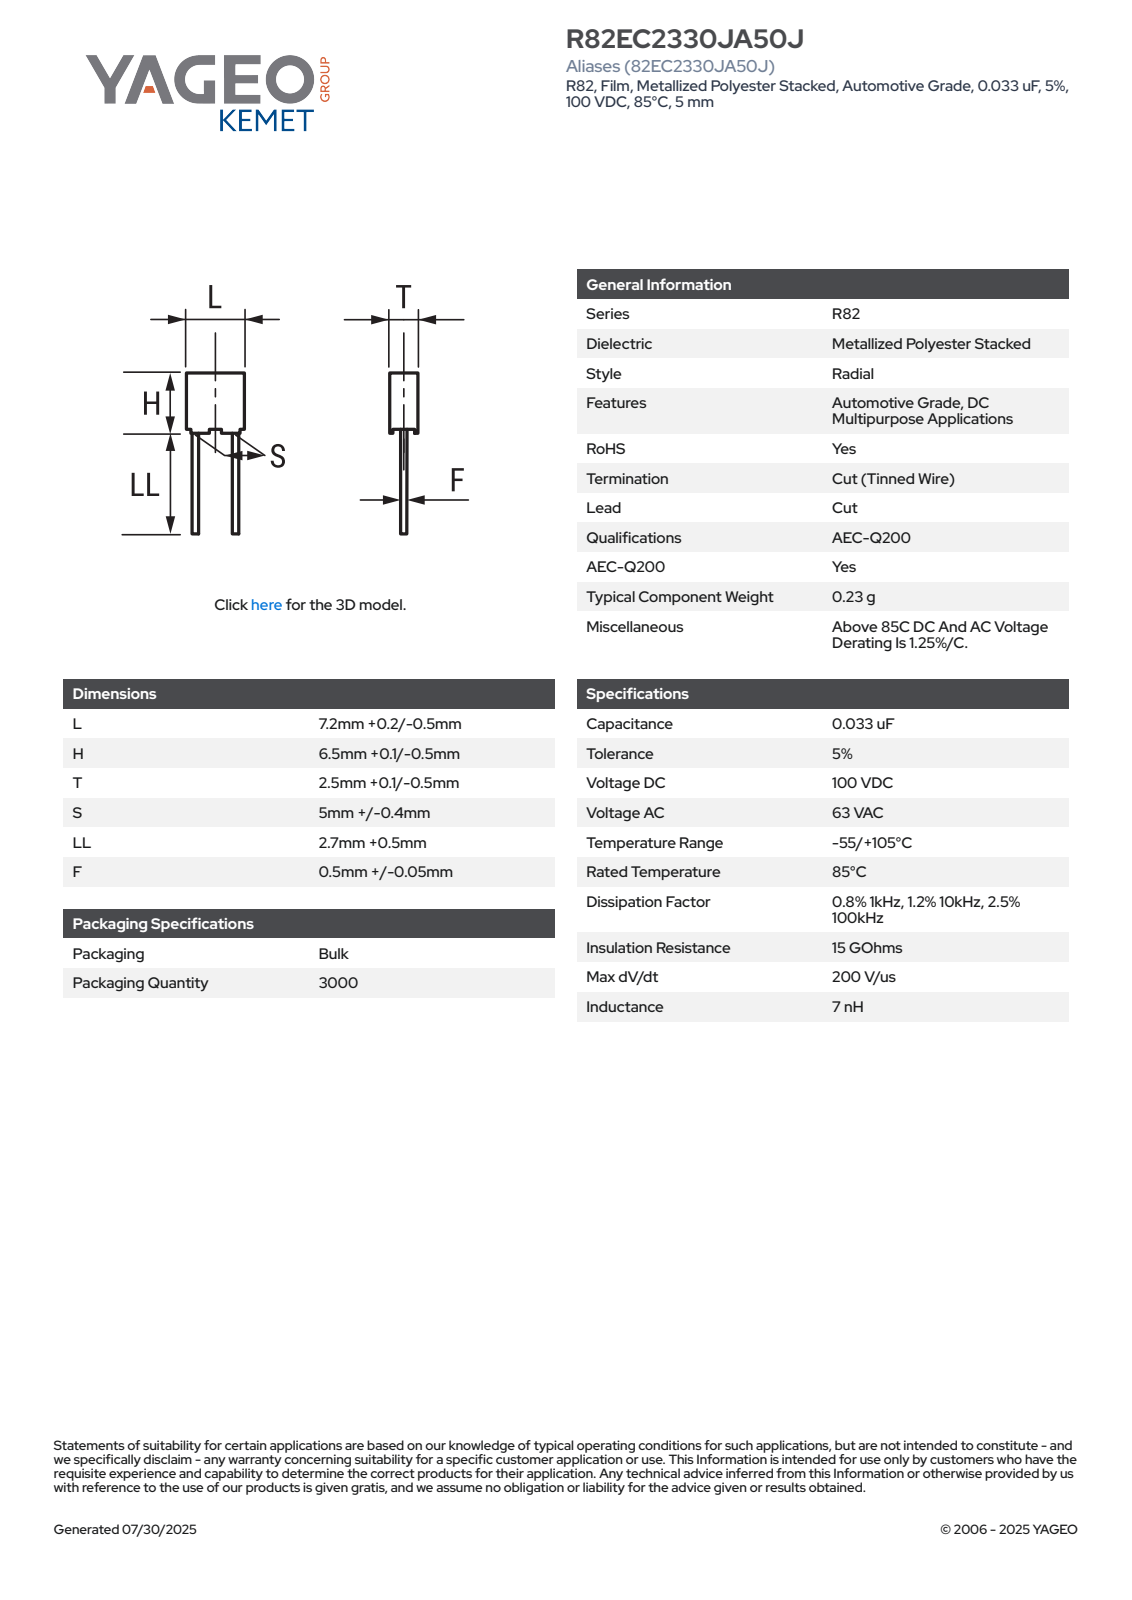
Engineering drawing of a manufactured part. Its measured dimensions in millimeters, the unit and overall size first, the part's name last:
Units: millimetres
Overall size (bounding box): 9.8 × 7.4 × 2.6
Round bosses / shafts (diameter × count): ⌀0.55 ×2
Partial cylindrical surfaces — rounded edges, fillets, slot ends (radius × count): R0.5 ×4
Main face-to-face distances: 2.6, 7.4, 5.85, 2.35, 2.1, 0.75, 6.6, 7.15, 6.9, 0.52
Volume: 117 mm³ · Surface area: 196 mm²
Bodies: 4 solids, 85 faces (77 planar, 8 cylindrical, 0 other)
Part name (STEP PRODUCT): CFR_RB3_7.2X6.5X2.5_L7.4H6.6T2.6S5LL3.2F0.55
STEP written by: SolidWorks 2014 (AUTOMOTIVE_DESIGN)
